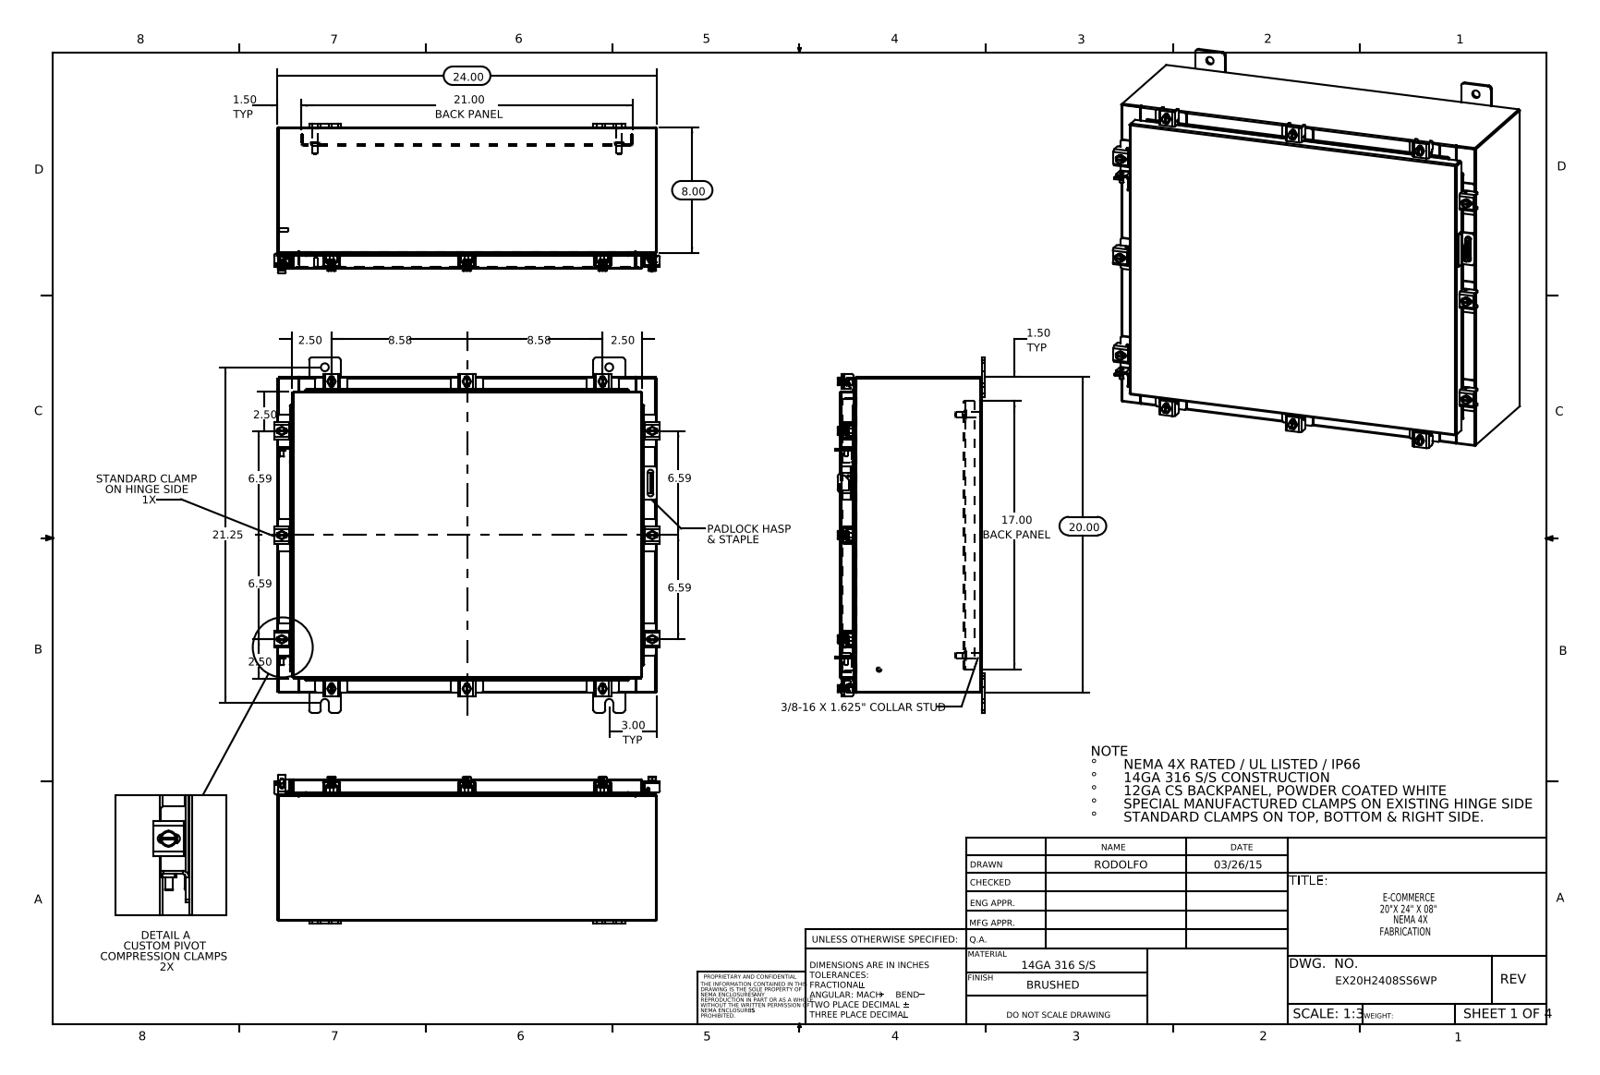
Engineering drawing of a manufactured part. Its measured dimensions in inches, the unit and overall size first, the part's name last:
Units: inches
Overall size (bounding box): 24.421 × 22.5 × 9.453
Round holes (diameter × count): ⌀0.213 ×12, ⌀0.26 ×12, ⌀0.5 ×8, ⌀0.125 ×1, ⌀0.25 ×1
Round bosses / shafts (diameter × count): ⌀0.5 ×12, ⌀0.25 ×12, ⌀0.399 ×10, ⌀0.625 ×4, ⌀0.375 ×4, ⌀0.33 ×4, ⌀0.315 ×2, ⌀0.236 ×2
Partial cylindrical surfaces — rounded edges, fillets, slot ends (radius × count): R0.06 ×54, R0.013 ×24, R0.141 ×24, R0.19 ×24, R0.088 ×22, R0.12 ×22, R0.09 ×18, R0.05 ×17
Main face-to-face distances: 0.075, 8.9, 8.975, 8.826, 19.925, 0.104, 1, 1.075, 7.826, 7.9
Hole centre spacings: 2.347, 4.44, 6.594, 10.222, 14.373, 16.62, 17.382, 20.544
Volume: 186.7 in³ · Surface area: 4 676 in²
Bodies: 81 solids, 2018 faces (1075 planar, 783 cylindrical, 160 other)
Part name (STEP PRODUCT): ATEX CLAMP HINGE BRAKET; 30X10 Clamp Bracket2; Quarter-20 CD Stud; EX20H2408SS6WP Backpanel (+8 more)
STEP written by: SolidWorks 2014 (CONFIG_CONTROL_DESIGN)
